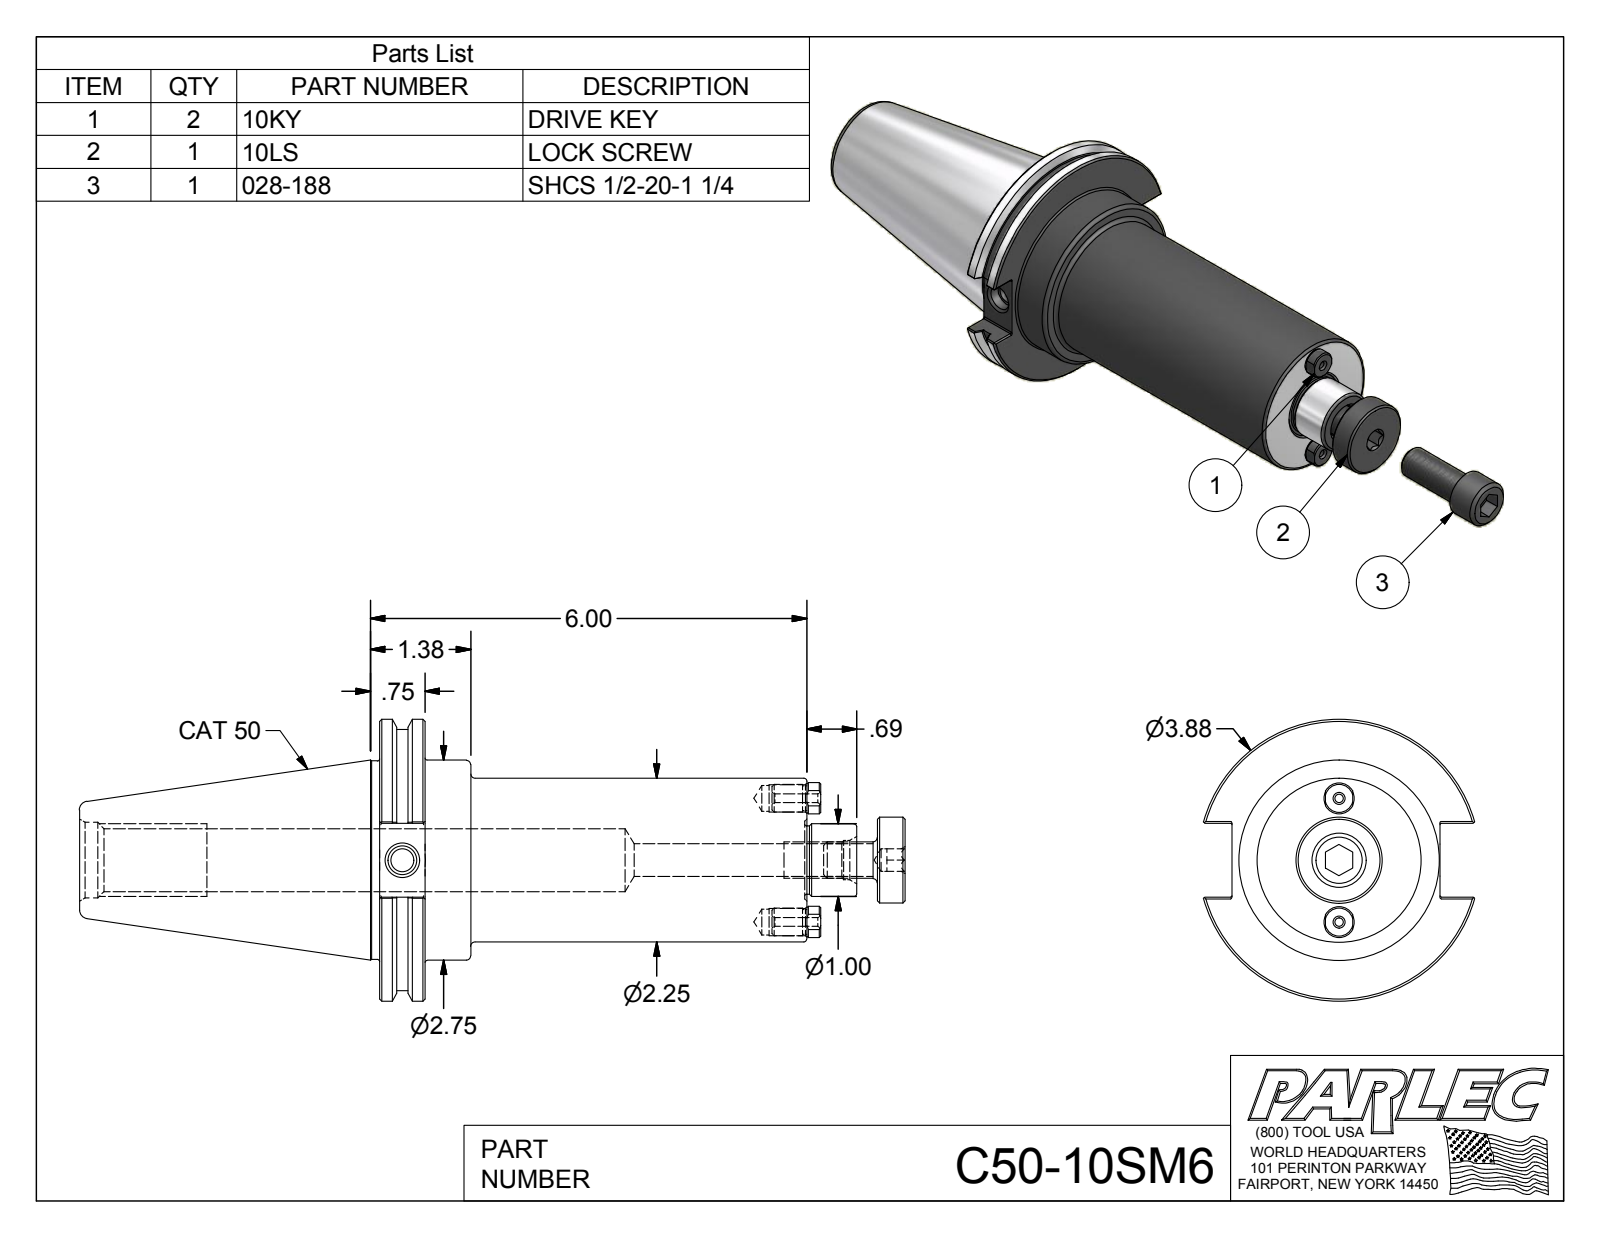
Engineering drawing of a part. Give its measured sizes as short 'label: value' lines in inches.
name: C50-10SM6; C50-10SM6-1; 10KY; 028-188 (+1 more)
written by: Autodesk Inventor 2012 (AUTOMOTIVE_DESIGN)
unit: in
bodies: 5 solids, 177 faces (68 planar, 48 cylindrical, 61 other)
size: 13.878 × 3.875 × 3.729
volume: 40.8 in³; area: 133.6 in²
holes: 2× ⌀0.12, 2× ⌀0.354, 2× ⌀0.374, 1× ⌀0.312, 1× ⌀0.315, 1× ⌀0.399, 1× ⌀0.446, 1× ⌀0.54, 1× ⌀0.865, 1× ⌀1.038
bosses: 2× ⌀0.38, 2× ⌀0.34, 1× ⌀3.875, 1× ⌀3.594, 1× ⌀2.75, 1× ⌀2.73, 1× ⌀2.25, 1× ⌀1.18
rounds: 12× R0.02, 2× R0.214
face distances: 0.625, 5.875, 5.25, 1.255, 0.63, 4.62, 7.224, 6.598, 5.969, 1.348
hole spacings: 0.85, 1.7
